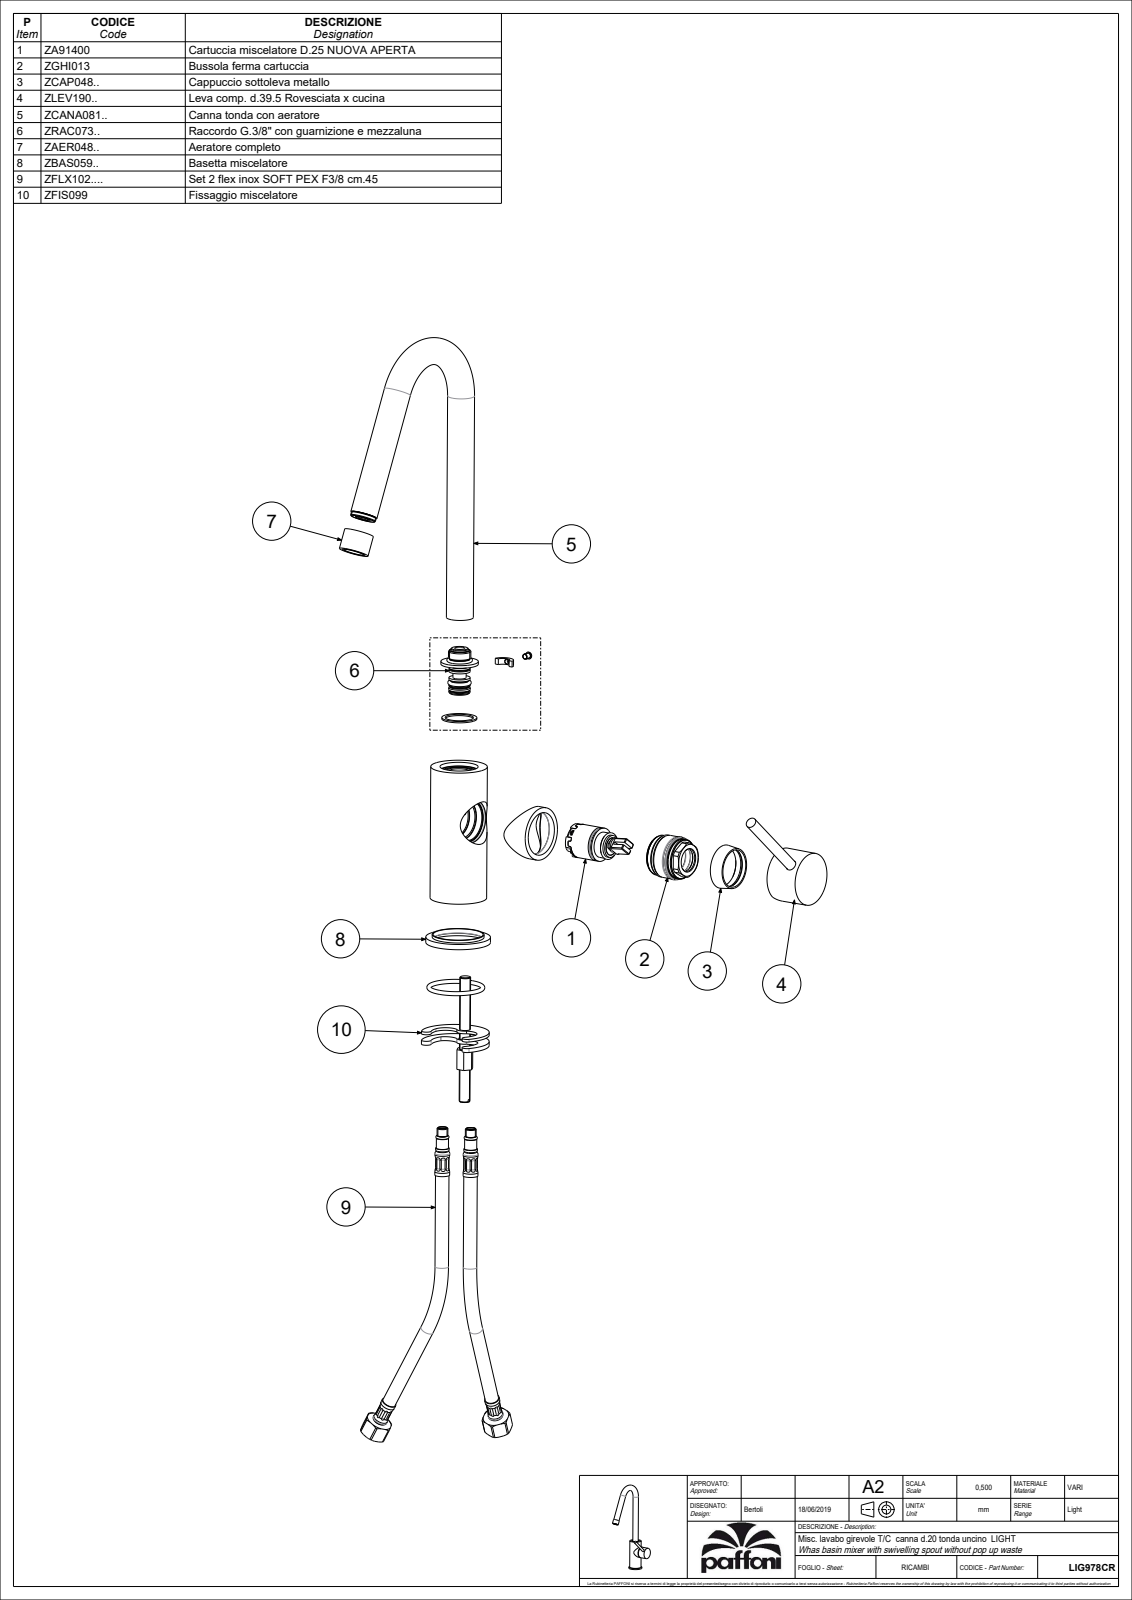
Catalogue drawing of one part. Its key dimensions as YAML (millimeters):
part_name: "LIG978CR"
step_written_by: "CREO PARAMETRIC BY PTC INC, 2020044 (CONFIG_CONTROL_DESIGN)"
units: millimeters
bodies: {solids: 0, faces: 111, planar: 45, cylindrical: 45, other: 21}
overall_size: [323.5, 158.72, 79.15]
round_holes:
  - {diameter: 3, count: 1}
round_bosses_or_shafts:
  - {diameter: 20, count: 2}
  - {diameter: 48, count: 1}
  - {diameter: 42, count: 1}
  - {diameter: 39.5, count: 1}
  - {diameter: 22, count: 1}
  - {diameter: 7.9, count: 1}
  - {diameter: 7.6, count: 1}
  - {diameter: 5, count: 1}
partial_cylinders:
  - {radius: 1, count: 8}
  - {radius: 0.8, count: 2}
  - {radius: 2.75, count: 1}
  - {radius: 3.5, count: 1}
  - {radius: 5, count: 1}
  - {radius: 6.4, count: 1}
face_to_face_distances: [4, 104, 100, 10, 25.15, 15.15, 15, 24.15, 14.15, 1]
